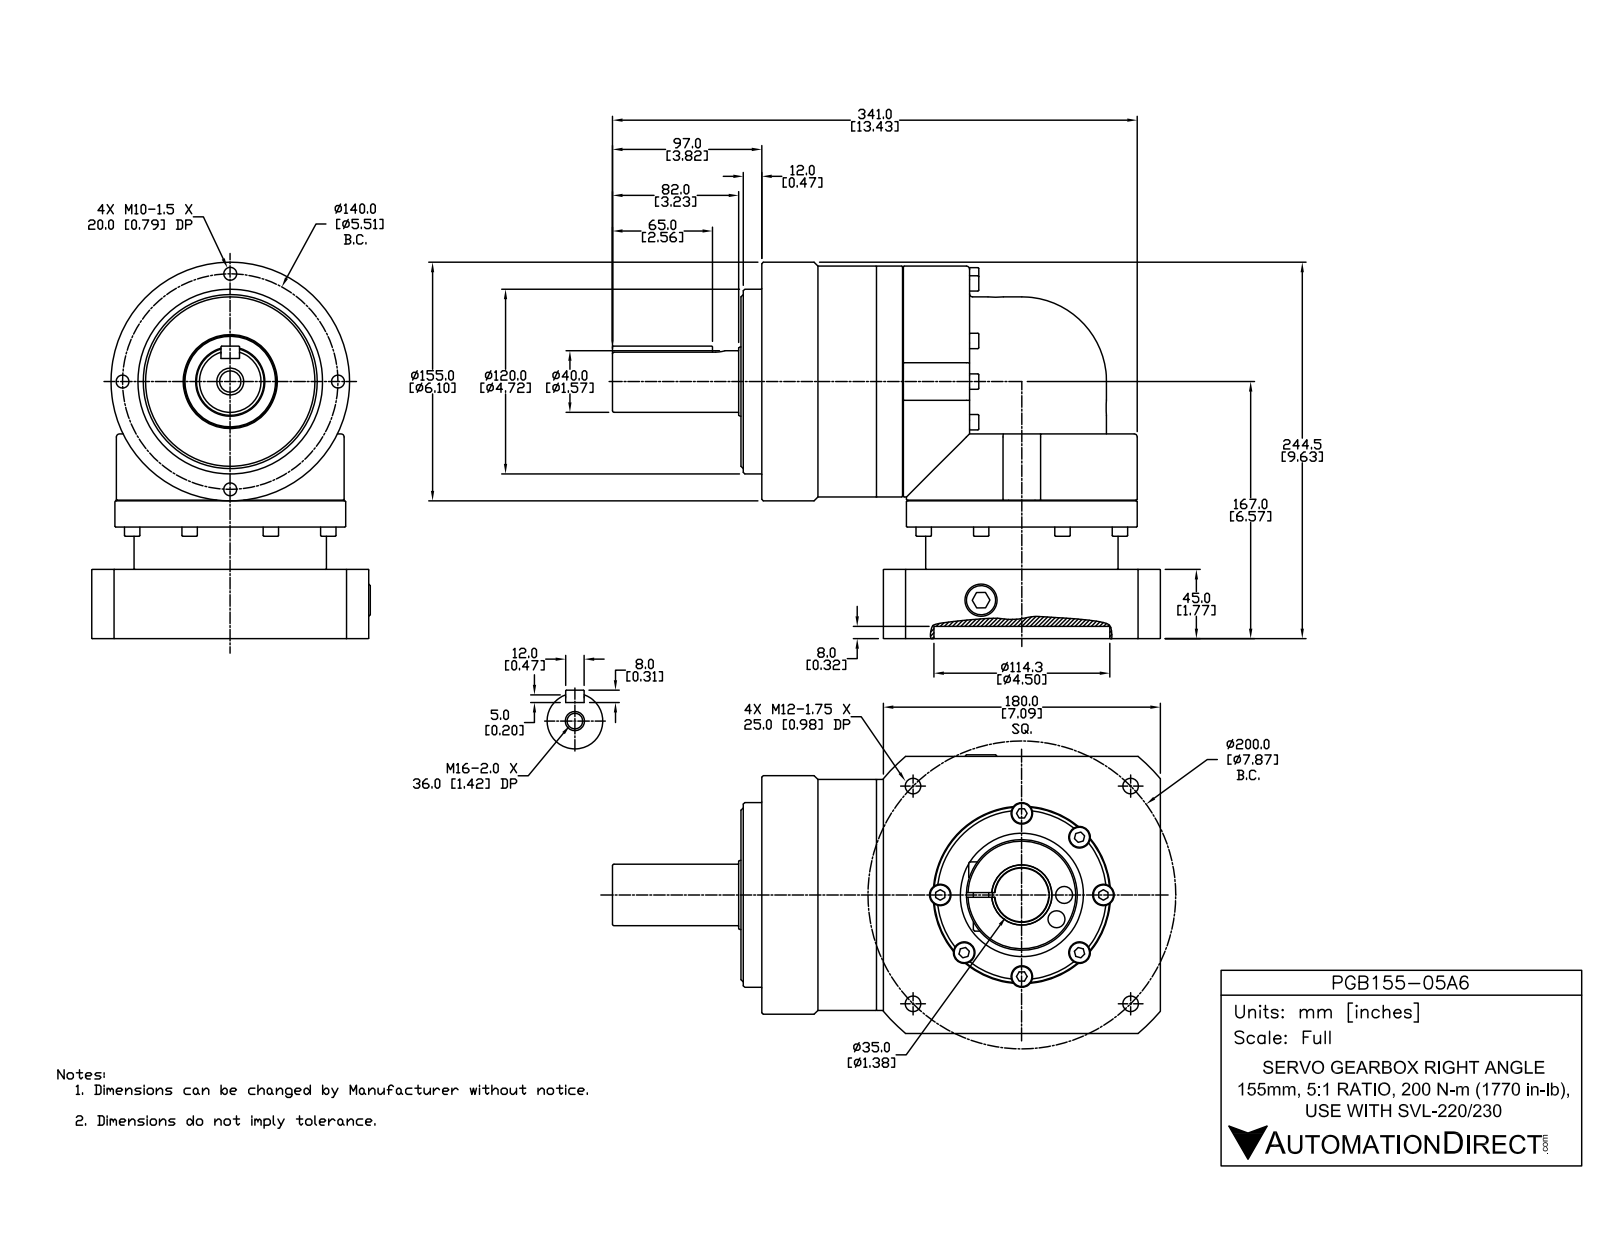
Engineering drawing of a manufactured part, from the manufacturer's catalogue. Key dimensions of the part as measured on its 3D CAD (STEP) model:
Part name (STEP PRODUCT): PGB155-05A6
STEP written by: SolidWorks 2014 (AUTOMOTIVE_DESIGN)
Units: inches
Bodies: 1 solid, 778 faces (333 planar, 202 cylindrical, 243 other)
Overall size (bounding box): 14.016 × 9.626 × 7.126
Volume: 344.2 in³ · Surface area: 475.9 in²
Round holes (diameter × count): ⌀0.256 ×8, ⌀0.551 ×7, ⌀0.33 ×4, ⌀0.398 ×4, ⌀0.433 ×3, ⌀0.394 ×2, ⌀0.545 ×1, ⌀0.689 ×1, ⌀1.378 ×1, ⌀3.15 ×1, ⌀4.331 ×1
Round bosses / shafts (diameter × count): ⌀0.394 ×18, ⌀0.236 ×8, ⌀0.512 ×7, ⌀5.906 ×2, ⌀5.827 ×2, ⌀6.102 ×1, ⌀4.921 ×1, ⌀4.724 ×1
Partial cylindrical surfaces — rounded edges, fillets, slot ends (radius × count): R0.079 ×6, R0.165 ×1, R0.236 ×1, R2.165 ×1, R2.25 ×1, R4.626 ×1
Main face-to-face distances: 1.772, 7.087, 3.642, 3.11, 10.728, 10.197, 0.531, 2.854, 3.819, 0.63
Hole centre spacings: 1.122, 4.009, 1.765, 2.087, 2.717, 2.719, 2.87, 3.833
